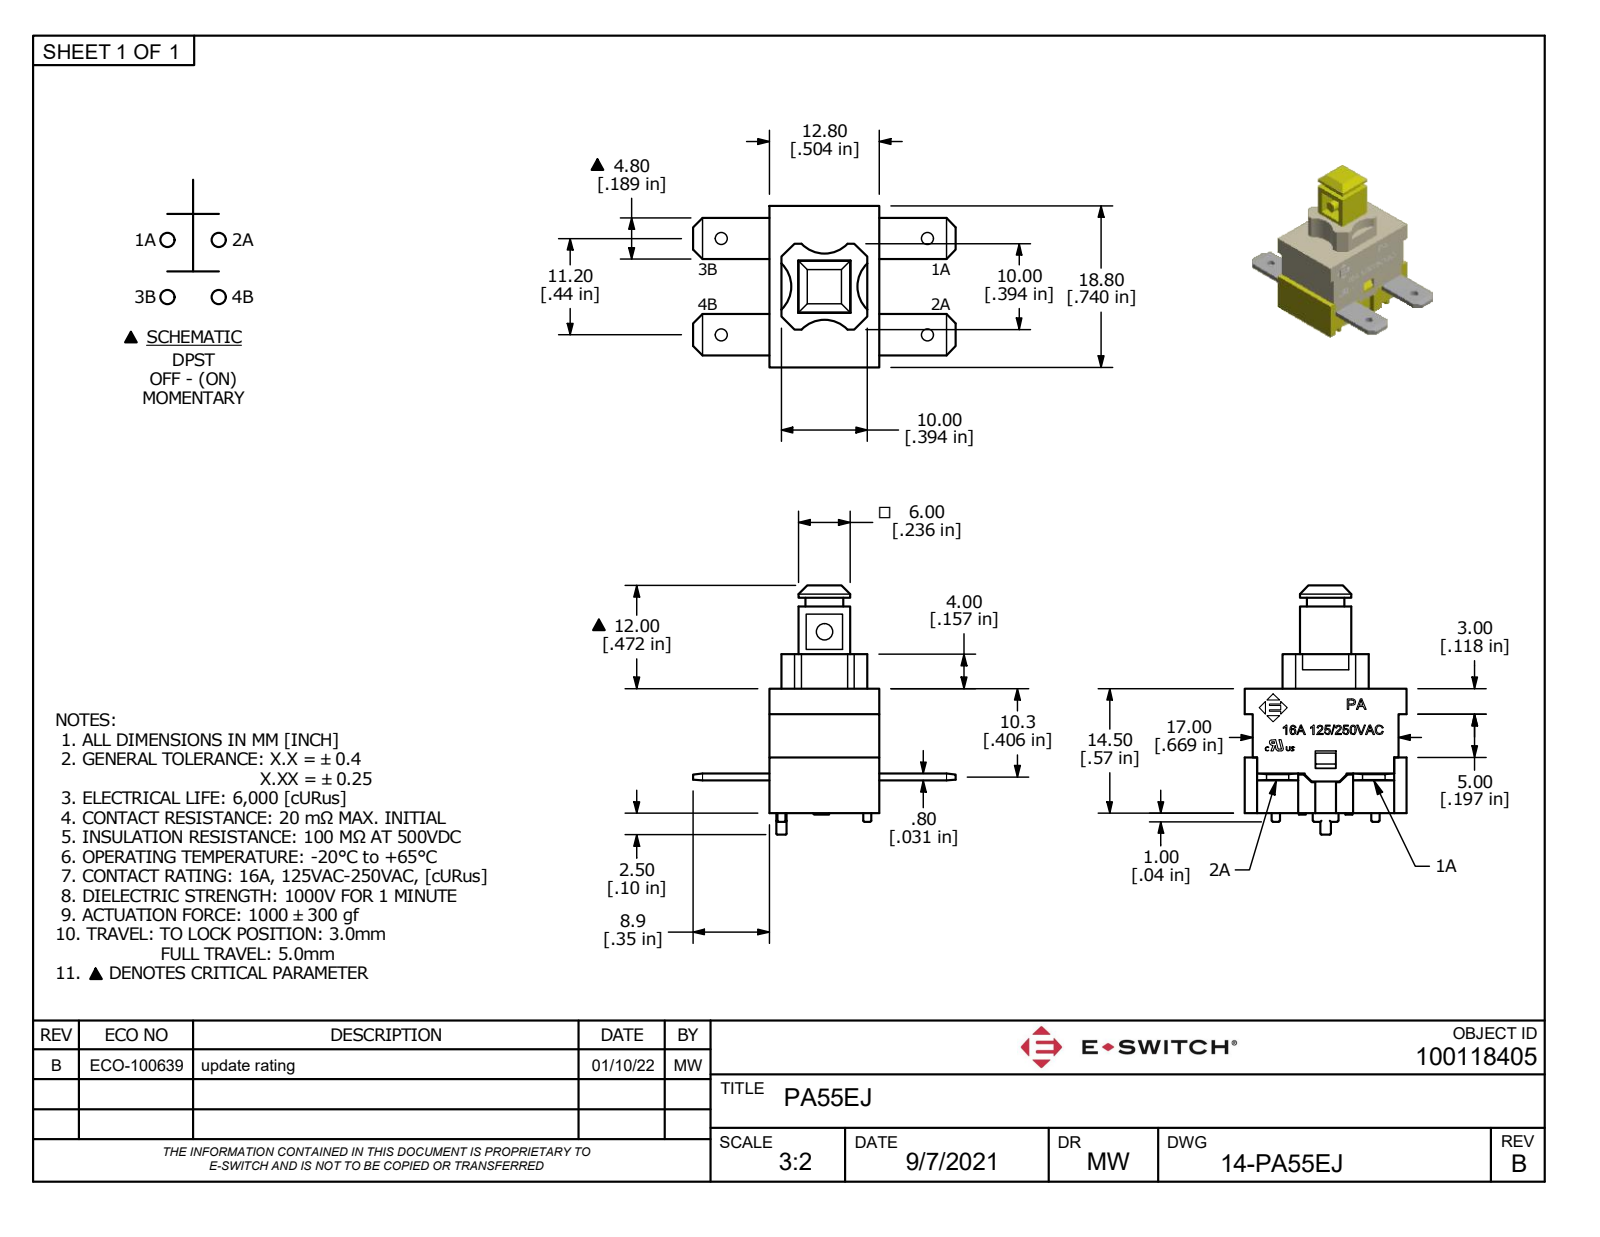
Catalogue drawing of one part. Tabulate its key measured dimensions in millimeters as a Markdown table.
| quantity | value |
| --- | --- |
| part name | PA55EJ |
| STEP written by | Autodesk Inventor 2022 (AUTOMOTIVE_DESIGN) |
| units | millimeters |
| bodies | 1 solid, 836 faces (622 planar, 83 cylindrical, 131 other) |
| overall size | 30.6 × 29 × 18.8 |
| volume | 2 244 mm³ |
| surface area | 4 613 mm² |
| round holes (diameter × count) | 1.4 × 4, 3 × 1 |
| round bosses / shafts (diameter × count) | 0.95 × 4, 2.5 × 2, 1.9 × 1 |
| partial cylindrical surfaces (radius × count) | 0.25 × 23, 0.12 × 16, 0.15 × 8, 3.71 × 4, 1 × 2, 0.5 × 1, 1.79 × 1, 2.32 × 1 |
| main face-to-face distances | 0.8, 12, 0.9, 16.8, 2, 3.8, 11.2, 11.05, 8.6, 4.4 |
| hole center spacings | 13.24, 11.2, 24, 26.48 |
